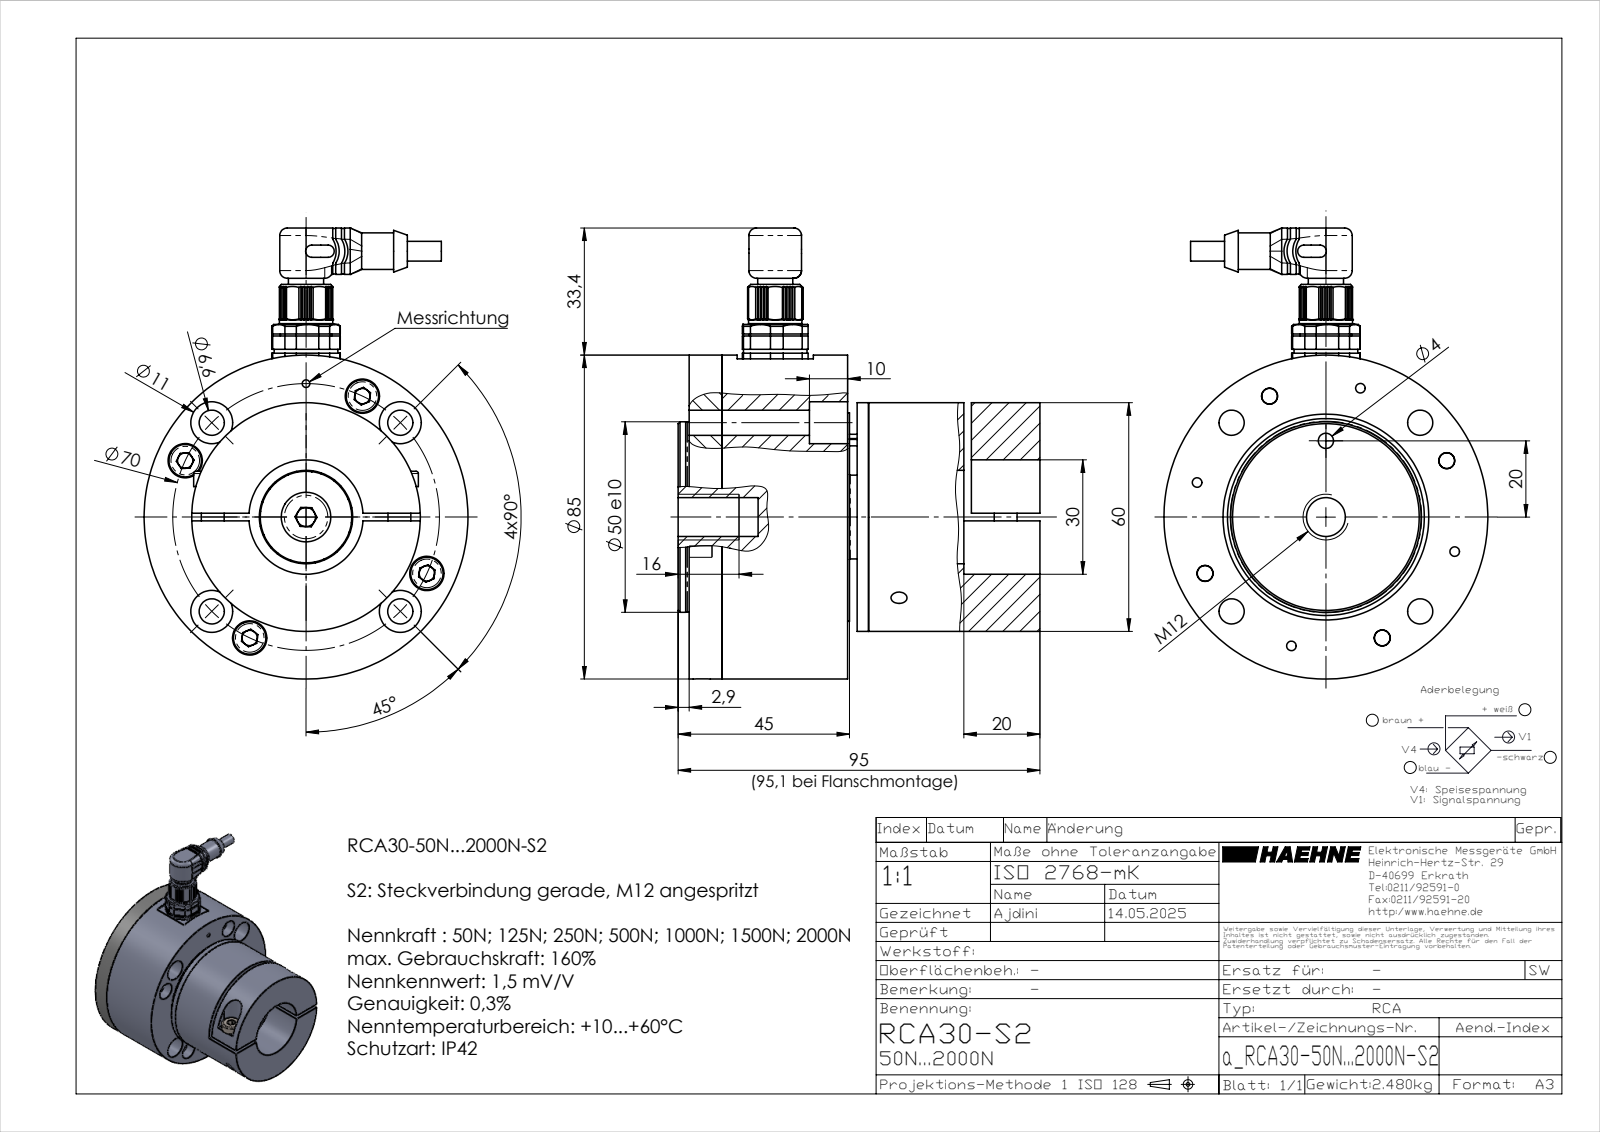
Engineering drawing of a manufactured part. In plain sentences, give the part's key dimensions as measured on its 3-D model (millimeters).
The part is named "RCA30 Oberteil_30; inafag_1203-tvh_7zkvytp7yxkimpdvw8sj0b5w4_24; inafag_1203-tvh_7zkvytp7yxkimpdvw8sj0b5w4_03; DIN EN ISO 8747-M3x10-St_DIN EN ISO 8747-M3x10-St (+8 more)". Its 3-D file was written by "SolidWorks 2023 (AUTOMOTIVE_DESIGN)". It is 53 solids with 1226 faces: 662 planar, 295 cylindrical and 269 other. Overall it measures 118.35 by 95.1 by 85 millimeters. Its volume is 361 986 cubic millimeters and its surface area 112 593 square millimeters. Round holes: 9 of diameter 3.4, 8 of diameter 2.5, 6 of diameter 6.6, 5 of diameter 4.2, 5 of diameter 11, 4 of diameter 1.1, 4 of diameter 1.15, 4 of diameter 1.6, 4 of diameter 1.85, 4 of diameter 4, 4 of diameter 5.3, 4 of diameter 9. Round bosses or shafts: 9 of diameter 3, 8 of diameter 5.7, 4 of diameter 8.5, 4 of diameter 5, 4 of diameter 1.8, 4 of diameter 1.55, 4 of diameter 1.5, 4 of diameter 1. Partial cylindrical surfaces (rounded edges, fillets, slot ends): 16 of radius 0.2, 9 of radius 0.3, 4 of radius 0.4, 4 of radius 0.53, 4 of radius 1, 4 of radius 1.27, 4 of radius 6, 2 of radius 1.6. The main face-to-face distances are 3, 2, 8.6, 47.1, 11.6, 45, 50, 30, 35.5, 50.1. The hole center spacings are 35, 49.5, 24.78, 25.2, 32.8, 51.14, 56.46, 2.5.
